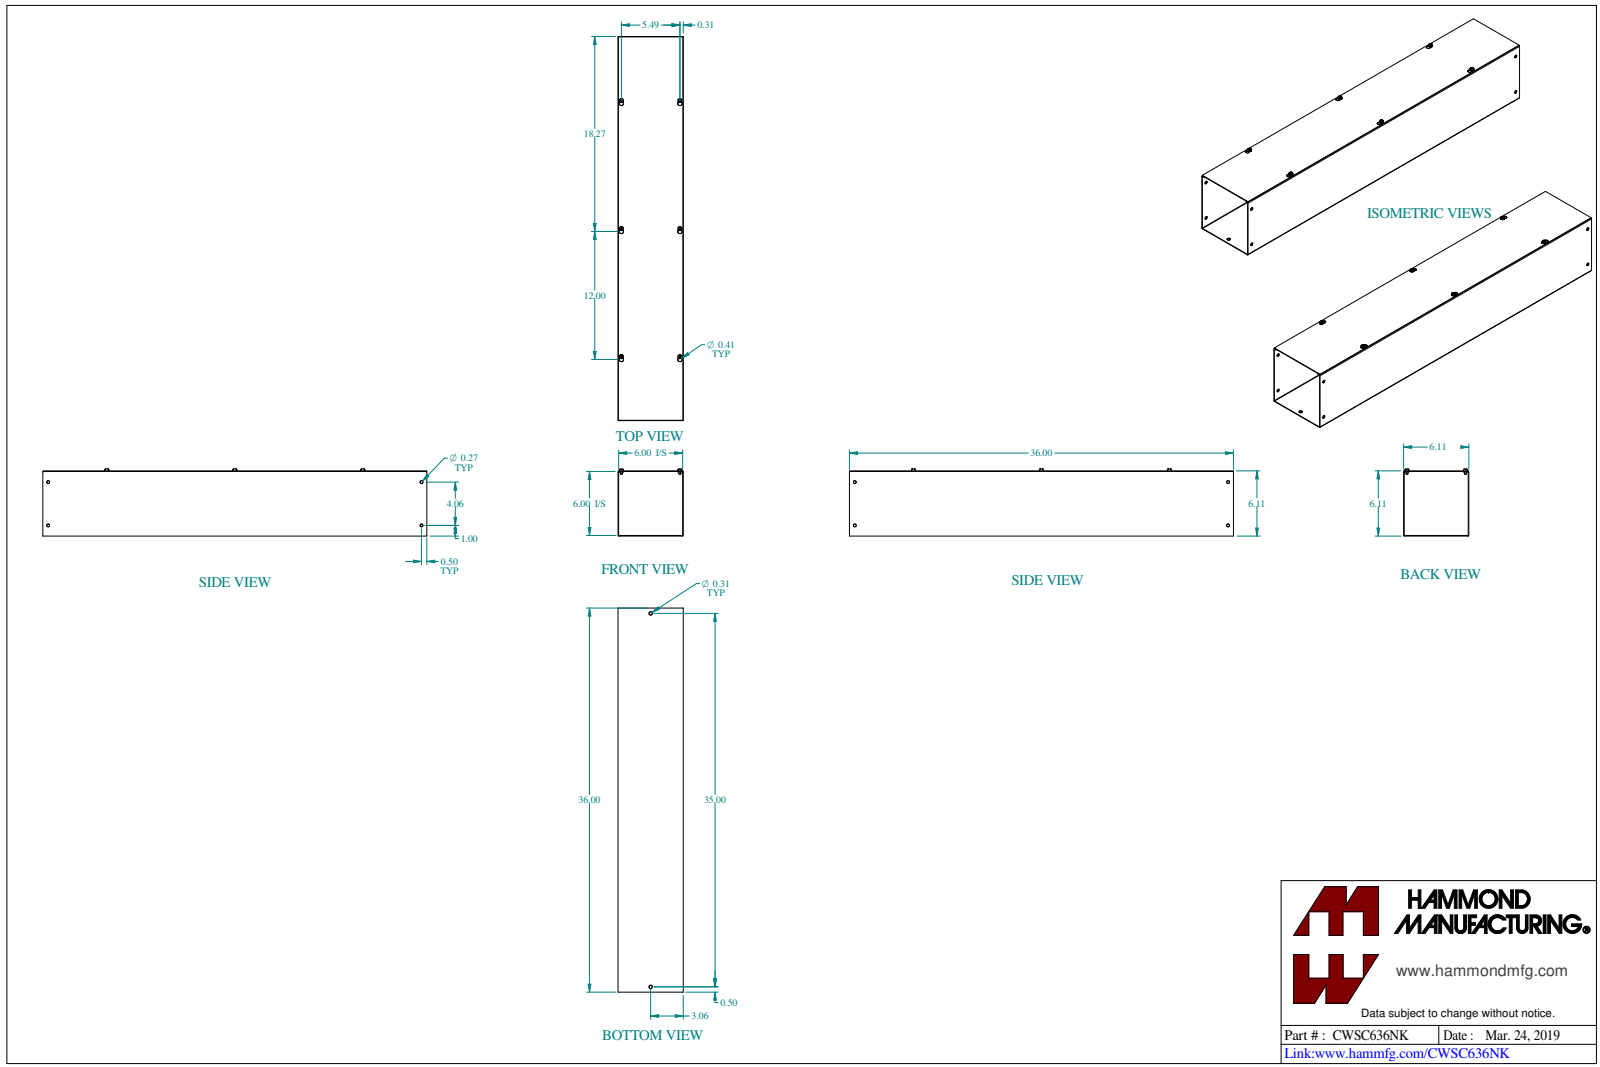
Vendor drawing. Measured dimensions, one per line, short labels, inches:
name: CWSC636NK
written by: SolidWorks 2023 (CONFIG_CONTROL_DESIGN)
unit: in
bodies: 8 solids, 242 faces (118 planar, 88 cylindrical, 36 other)
size: 36 × 6.289 × 6.114
volume: 51.17 in³; area: 1 806 in²
holes: 6× ⌀0.177, 4× ⌀0.266, 2× ⌀0.313
bosses: 6× ⌀0.375, 6× ⌀0.19
rounds: 6× R0.125, 6× R0.203, 4× R0.029, 4× R0.086
face distances: 0.057, 6.057, 6, 6.114, 5.943, 0.114, 0.031, 6.083, 0.026, 6.026
hole spacings: 6.147, 12, 13.196, 17.714, 29.628, 5.489, 35, 4.057
